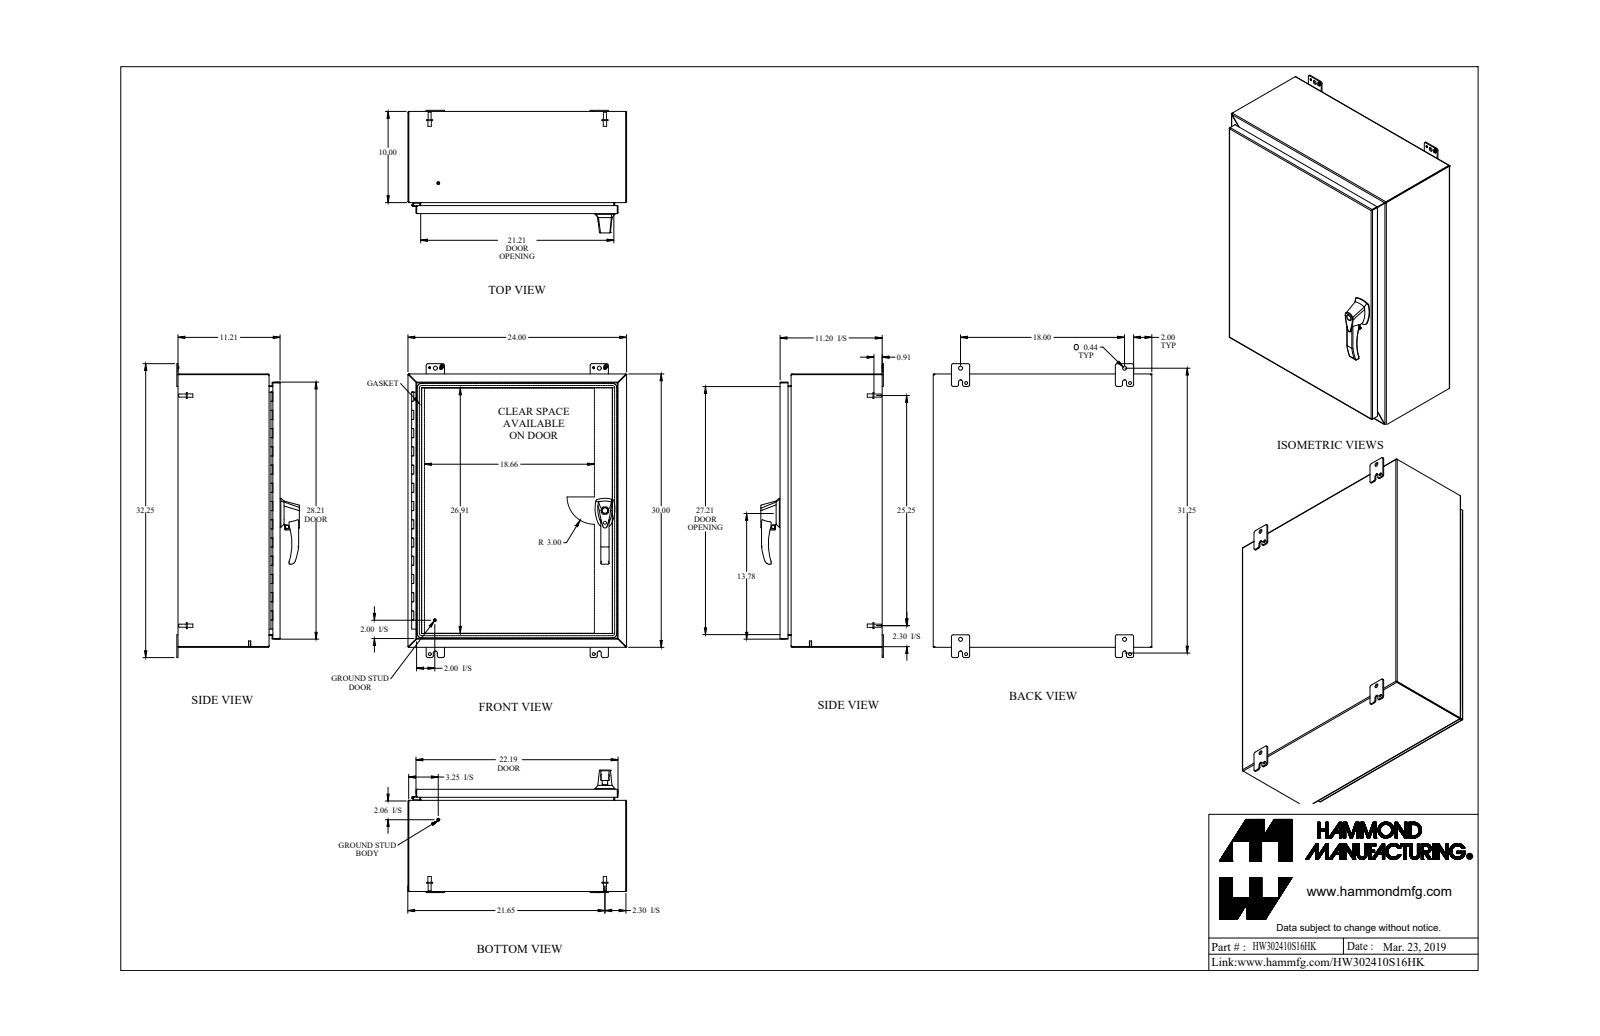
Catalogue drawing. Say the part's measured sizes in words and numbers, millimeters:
The part is named "HW302410S16HK". Its 3-D file was written by "SolidWorks 2018 (AUTOMOTIVE_DESIGN)". It is 42 solids with 1456 faces: 691 planar, 613 cylindrical and 152 other. Overall it measures 819.2 by 609.6 by 341.6 millimeters. Its volume is 3 851 000 cubic millimeters and its surface area 3 943 000 square millimeters. Round holes: 6 of diameter 4.5, 5 of diameter 8, 3 of diameter 6.4, 3 of diameter 6.7, 3 of diameter 10.5, 2 of diameter 5, 2 of diameter 6.5, 2 of diameter 10, 2 of diameter 11.1, 1 of diameter 2.8, 1 of diameter 5.9, 1 of diameter 8.4. Round bosses or shafts: 9 of diameter 9.5, 7 of diameter 6.4, 6 of diameter 4, 4 of diameter 16.5, 4 of diameter 8.4, 3 of diameter 25.4, 3 of diameter 13, 2 of diameter 16. Partial cylindrical surfaces (rounded edges, fillets, slot ends): 27 of radius 6.4, 24 of radius 4.8, 20 of radius 0.9, 20 of radius 2.7, 12 of radius 1.5, 9 of radius 3.2, 8 of radius 1.1, 8 of radius 5.5. The main face-to-face distances are 1.8, 1.8, 282.9, 281.1, 282.9, 284.7, 607.8, 760.2, 605.9, 609.6. The hole center spacings are 28.2, 282.4, 282.4, 564.8, 282.4, 457.2, 603.3, 797.1.
